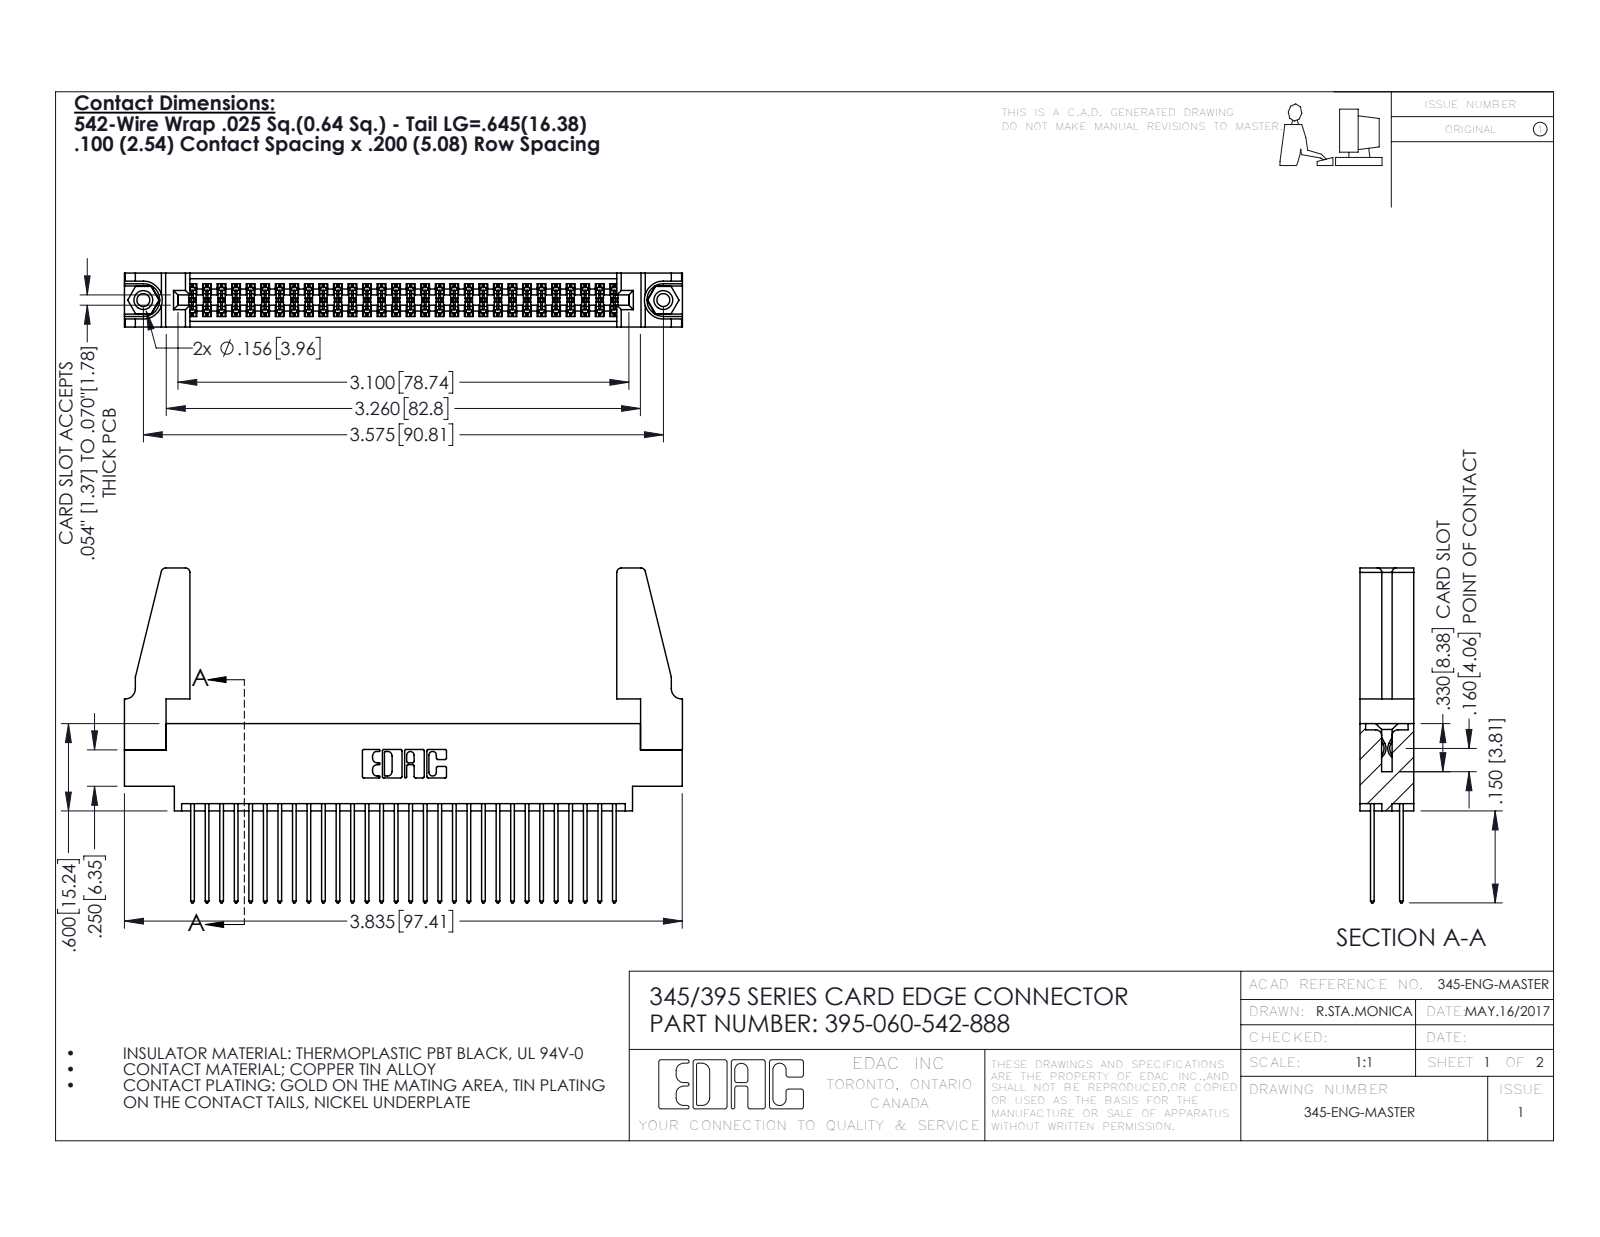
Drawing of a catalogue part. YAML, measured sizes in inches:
part_name: "345-292-001_345-293-142; 345-220-078_345-220-088; 345 Part_0.170 Offset - 0.156 Dia-TH; 345-250-001_345-250-001-102 (+1 more)"
step_written_by: "SolidWorks 2016 (CONFIG_CONTROL_DESIGN)"
units: inches
bodies: {solids: 65, faces: 3254, planar: 2136, cylindrical: 1102, other: 16}
overall_size: [3.836, 2.302, 0.37]
volume: 0.779
surface_area: 28.54
round_holes:
  - {diameter: 0.089, count: 2}
  - {diameter: 0.125, count: 2}
  - {diameter: 0.156, count: 2}
  - {diameter: 0.064, count: 1}
round_bosses_or_shafts:
  - {diameter: 0.155, count: 2}
partial_cylinders:
  - {radius: 0.006, count: 90}
  - {radius: 0.01, count: 60}
  - {radius: 0.01, count: 22}
  - {radius: 0.03, count: 8}
  - {radius: 0.007, count: 6}
  - {radius: 0.031, count: 6}
  - {radius: 0.026, count: 3}
  - {radius: 0.014, count: 2}
face_to_face_distances: [0.072, 0.298, 0.37, 0.2, 0.098, 0.272, 0.025, 0.225, 0.175, 0.149]
hole_center_spacings: [0.27, 3.34, 3.575]
